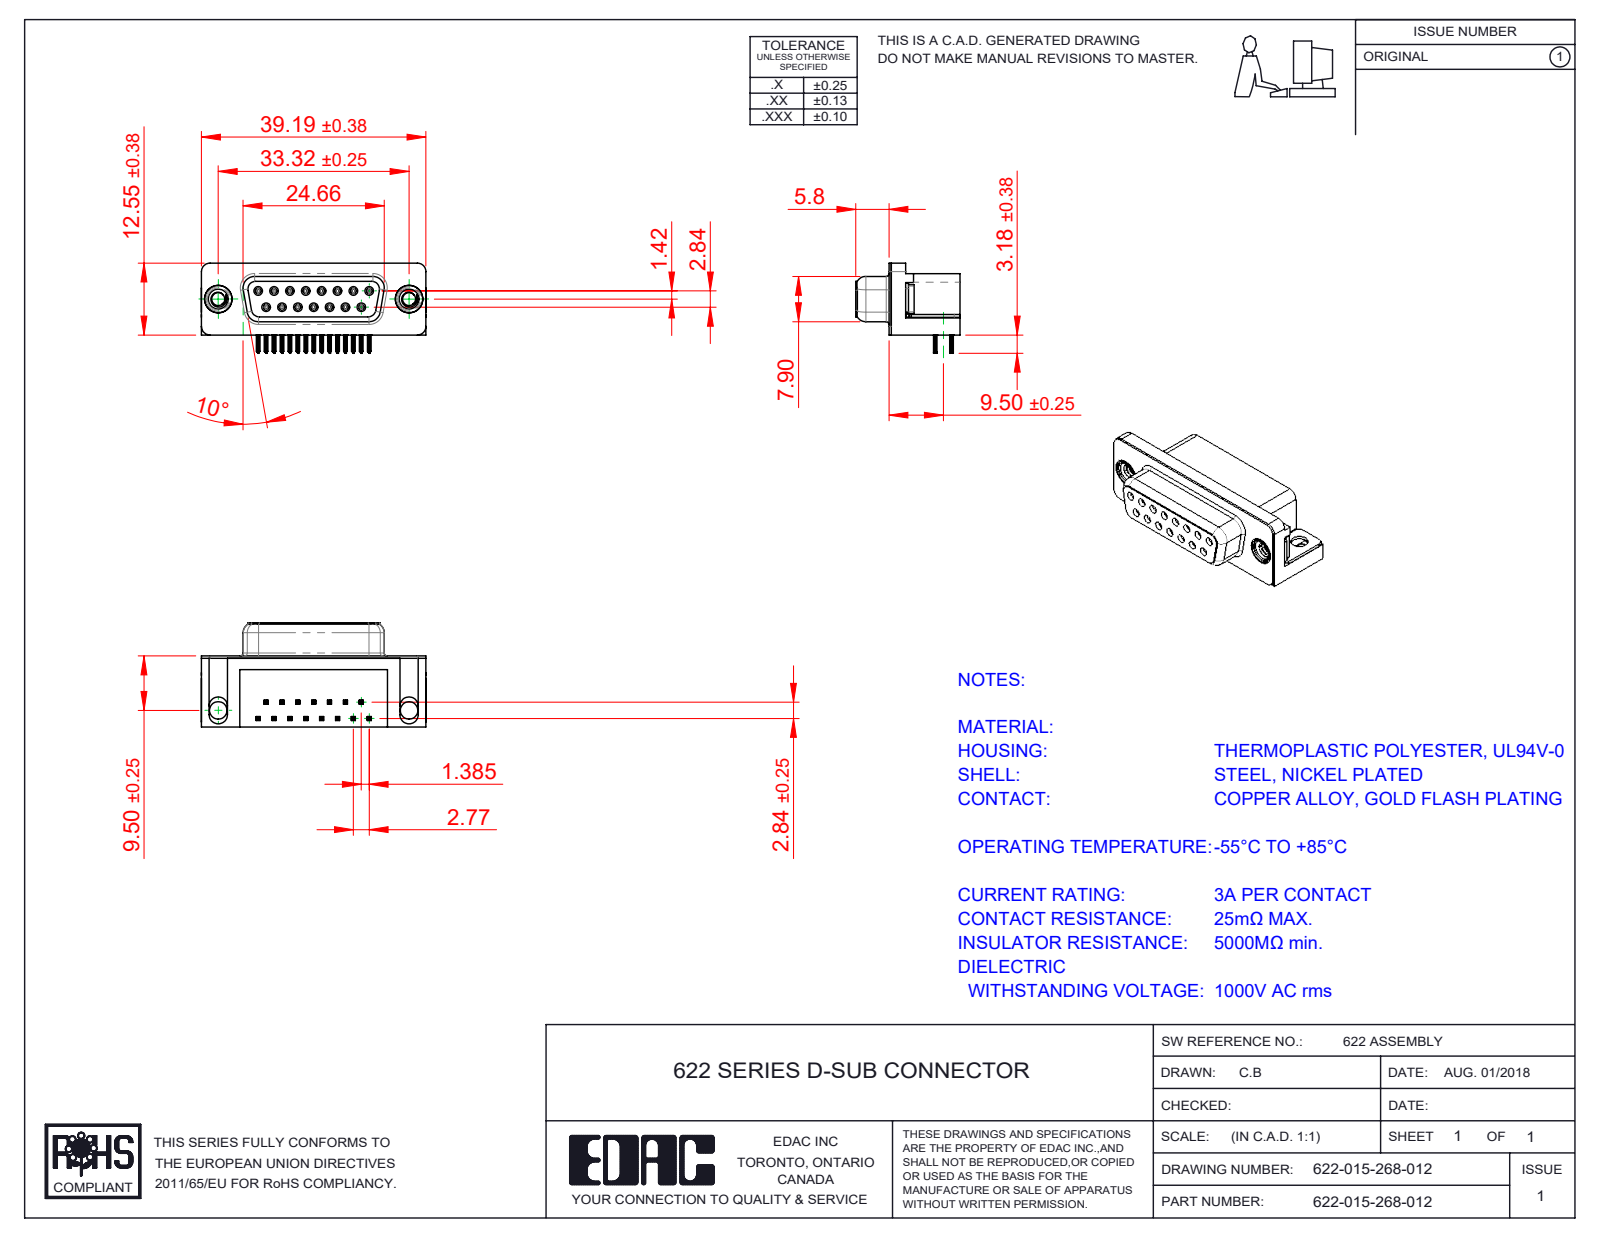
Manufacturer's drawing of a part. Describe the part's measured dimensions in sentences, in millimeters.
The part is named "622 Socket Bottom; 622 Contact Top; 622 4-40 Threaded Rivet; 622 Shell_15 Socket (+3 more)". Its 3-D file was written by "SolidWorks 2016 (CONFIG_CONTROL_DESIGN)". It is 21 solids with 2425 faces: 1072 planar, 605 cylindrical and 748 other. Overall it measures 39.22 by 18.2 by 15.73 millimeters. Its volume is 5 187 cubic millimeters and its surface area 6 703 square millimeters. Round holes: 15 of diameter 0.8, 15 of diameter 0.9, 2 of diameter 2.26, 2 of diameter 3.05, 2 of diameter 4, 2 of diameter 4.8, 2 of diameter 5. Round bosses or shafts: 15 of diameter 1.2, 2 of diameter 4.9, 2 of diameter 4.75, 2 of diameter 3.9. Partial cylindrical surfaces (rounded edges, fillets, slot ends): 120 of radius 0.1, 60 of radius 0.15, 30 of radius 0.35, 18 of radius 1, 15 of radius 0.34, 8 of radius 0.25, 8 of radius 1.35, 8 of radius 1.5. The main face-to-face distances are 0.4, 12, 6.2, 12.4, 10.35, 2.9, 6.65, 0.85, 0.35, 5.8. The hole center spacings are 3.16, 2.77, 5.54, 8.31, 11.08, 5.03, 5.04, 7.48.
